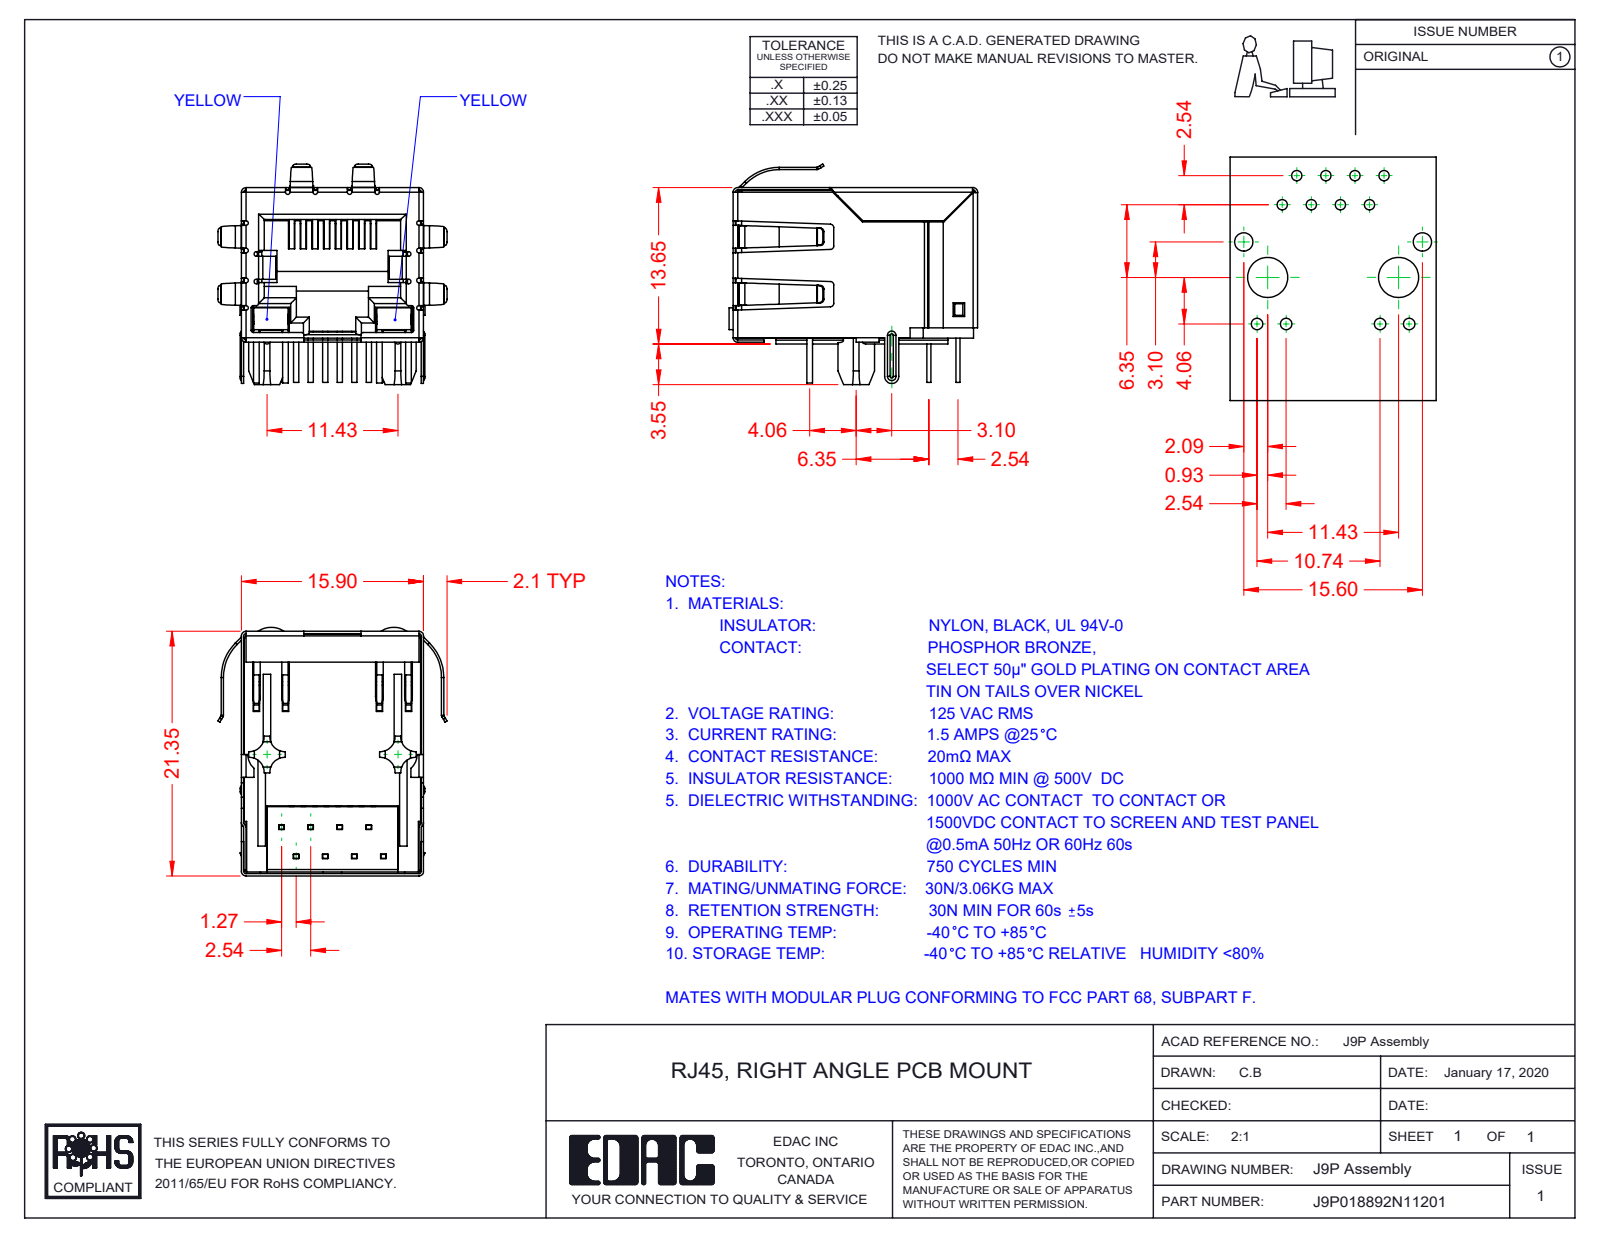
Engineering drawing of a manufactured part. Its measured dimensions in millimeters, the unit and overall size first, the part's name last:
Units: millimetres
Overall size (bounding box): 21.7 × 20 × 19.25
Partial cylindrical surfaces — rounded edges, fillets, slot ends (radius × count): R0.2 ×39, R0.5 ×22, R0.3 ×20, R0.4 ×16, R1.3 ×8, R0.23 ×5, R0.11 ×4, R0.31 ×4
Main face-to-face distances: 15.45, 15.7, 15.65, 0.35, 0.54, 15.5, 12.36, 0.6, 1.4, 0.59
Volume: 2 687 mm³ · Surface area: 7 515 mm²
Bodies: 13 solids, 1472 faces (1042 planar, 336 cylindrical, 94 other)
Part name (STEP PRODUCT): 9P-LED Contact Lock; 9P-LED Insulator; J9P018892N11202; 9P-LED Assembly (+4 more)
STEP written by: SolidWorks 2016 (CONFIG_CONTROL_DESIGN)
